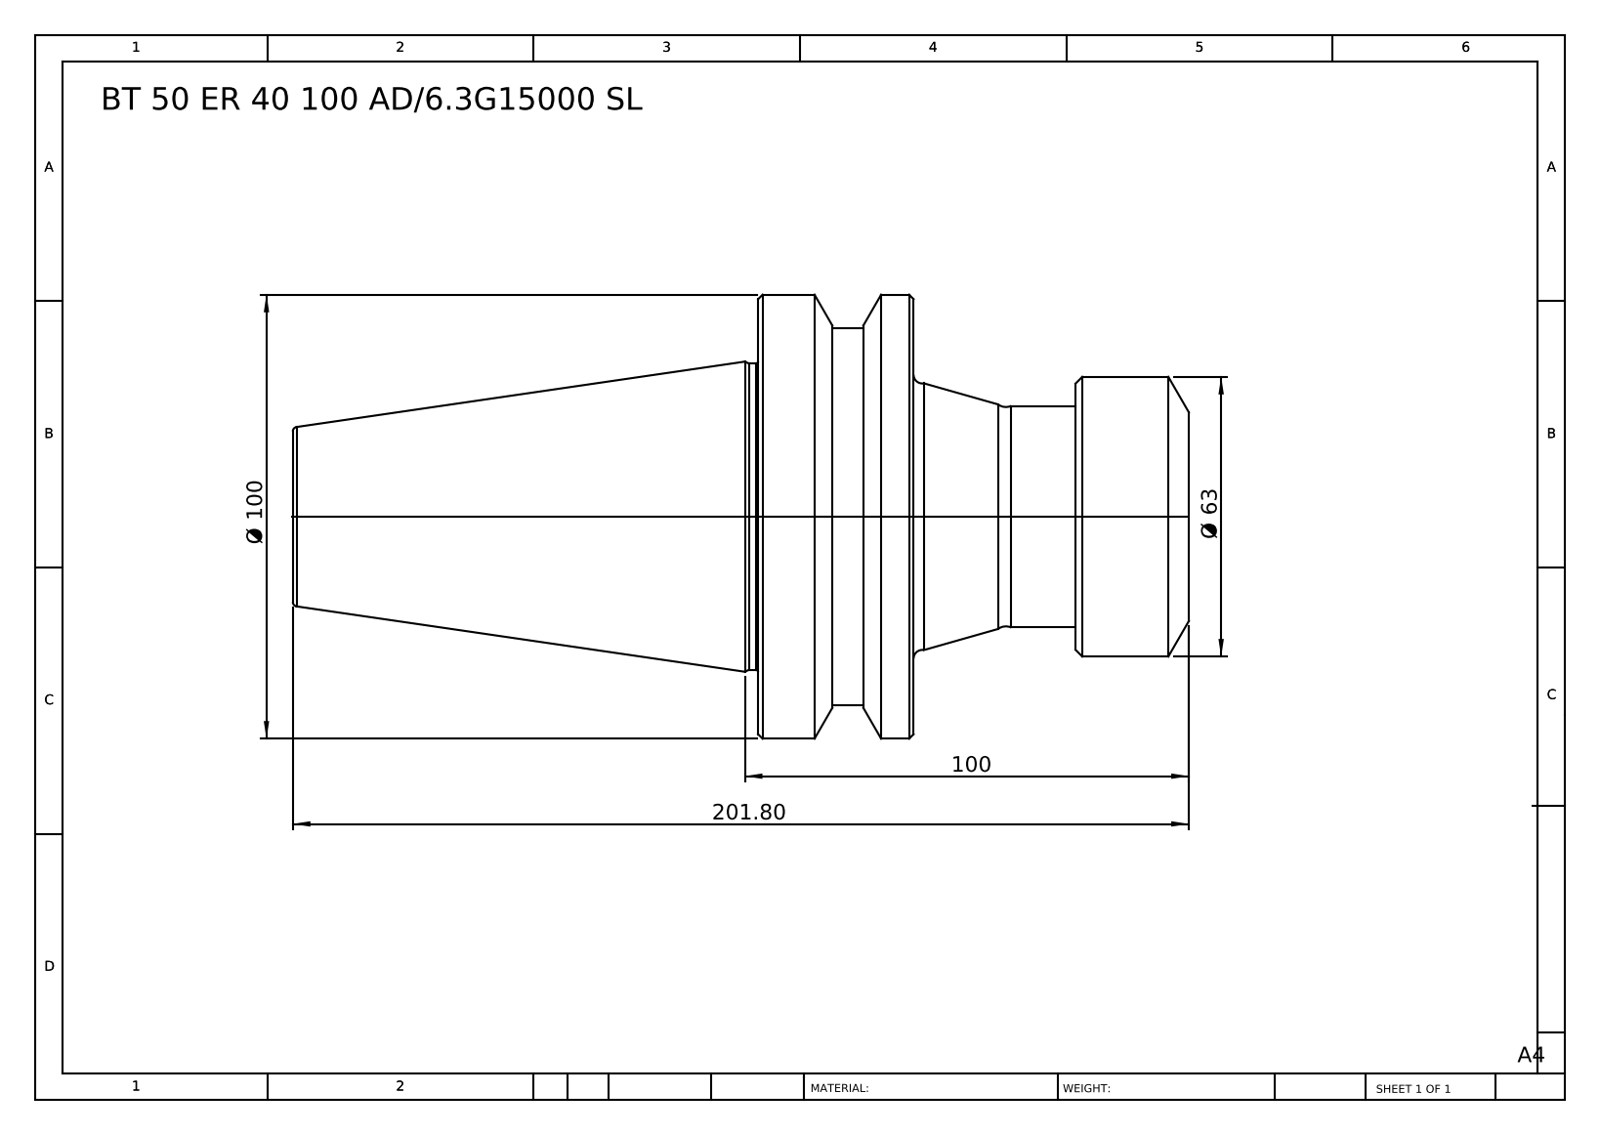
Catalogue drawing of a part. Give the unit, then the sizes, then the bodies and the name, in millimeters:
Units: millimetres
Overall size (bounding box): 201.8 × 100 × 100
Round bosses / shafts (diameter × count): ⌀100 ×1, ⌀85 ×1, ⌀69 ×1, ⌀63 ×1, ⌀49.9 ×1
Main face-to-face distances: 35, 62, 97, 201.8, 139.8, 104.8, 25.5, 36.5, 71.5, 176.3
Volume: 667 088 mm³ · Surface area: 56 048 mm²
Bodies: 1 solid, 49 faces (7 planar, 12 cylindrical, 30 other)
Part name (STEP PRODUCT): BT 50 ER 40 100 AD-6.3G15000 SL
STEP written by: SolidWorks 2014 (CONFIG_CONTROL_DESIGN)
